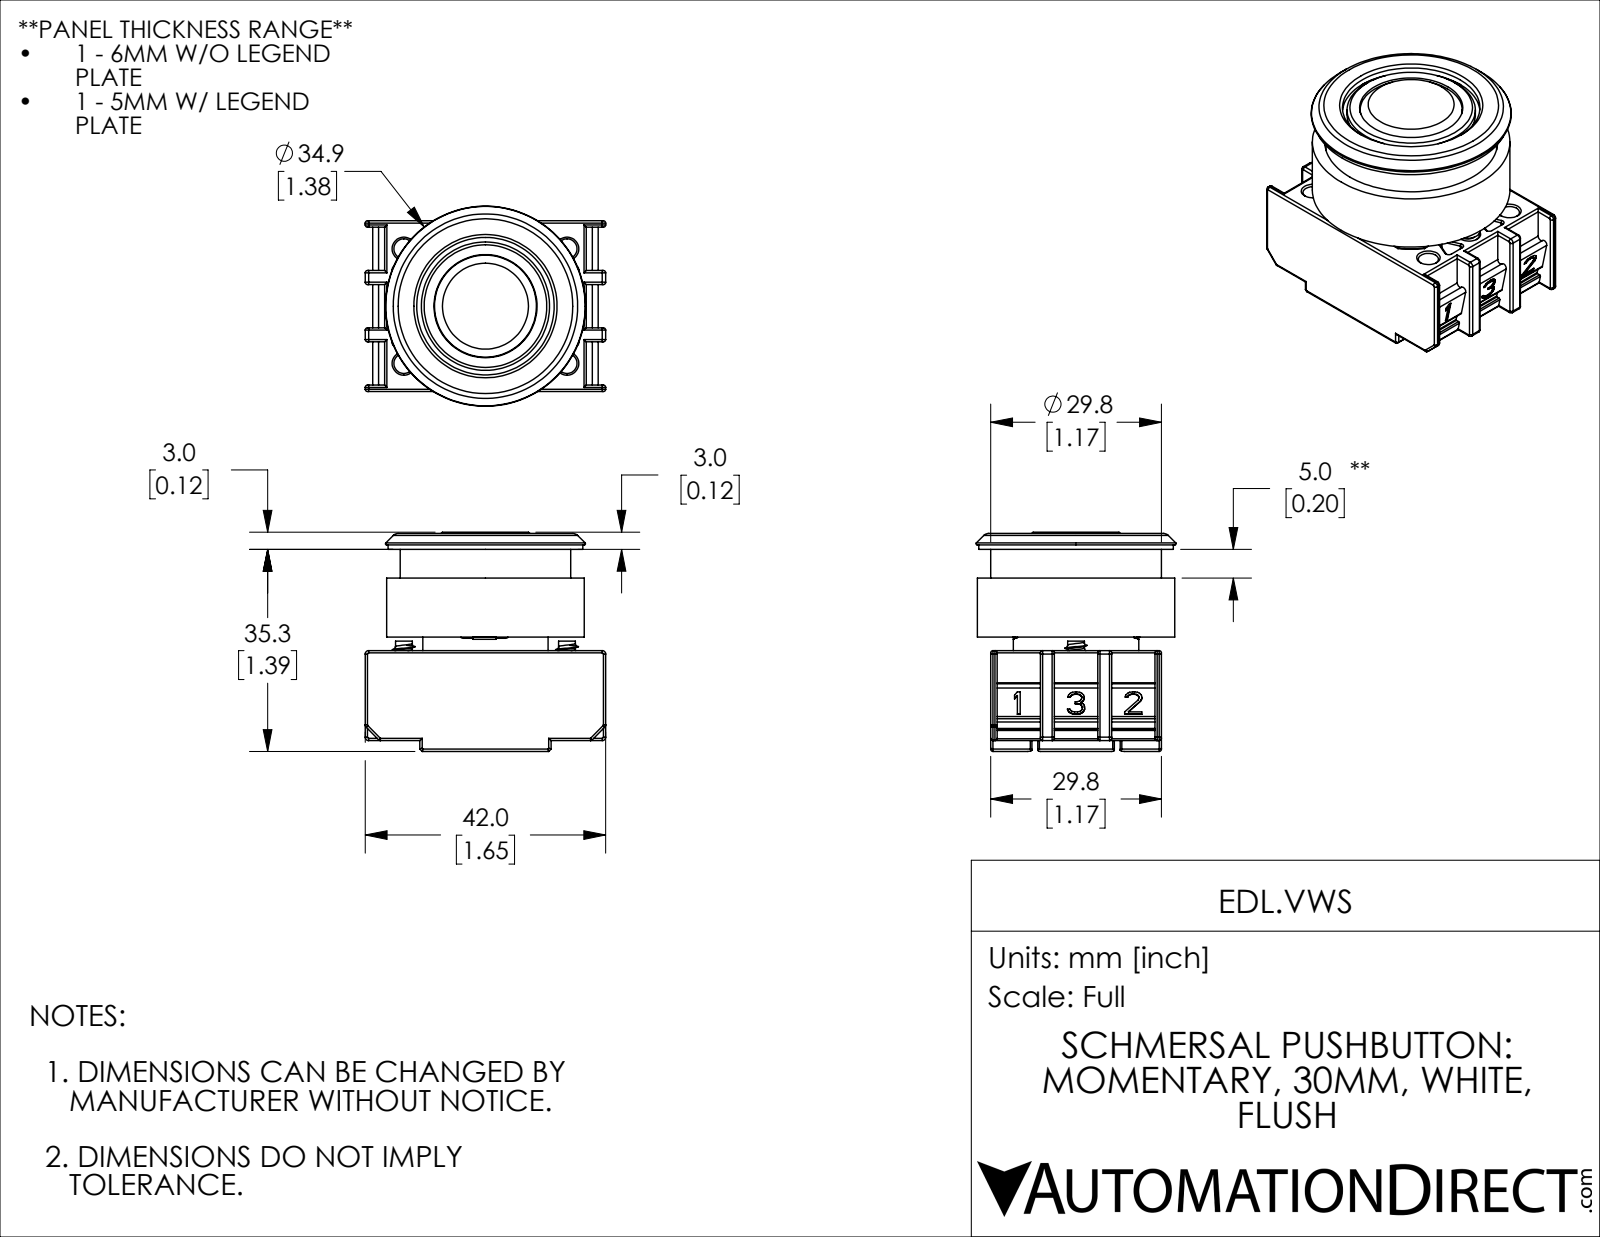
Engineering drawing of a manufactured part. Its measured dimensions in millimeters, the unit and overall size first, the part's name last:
Units: millimetres
Overall size (bounding box): 42 × 38.25 × 34.93
Round holes (diameter × count): ⌀3.5 ×6, ⌀5.15 ×6, ⌀10.4 ×1, ⌀13.1 ×1, ⌀18 ×1, ⌀24 ×1, ⌀24.2 ×1, ⌀27 ×1, ⌀30.2 ×1
Round bosses / shafts (diameter × count): ⌀4.8 ×2, ⌀2.93 ×2, ⌀34.5 ×1, ⌀34 ×1, ⌀29.8 ×1, ⌀22.4 ×1, ⌀21.9 ×1, ⌀17.8 ×1
Partial cylindrical surfaces — rounded edges, fillets, slot ends (radius × count): R0.4 ×112, R0.3 ×48, R0.2 ×32, R0.6 ×8, R0.5 ×6, R0.1 ×2, R0.6 ×2, R0.8 ×2
Main face-to-face distances: 29.8, 16.1, 19.95, 2.35, 10, 5, 1.9, 18.45, 10.3, 15.7
Hole centre spacings: 10, 17.41, 30.2, 28.5, 14.25, 20, 34.82
Volume: 25 195 mm³ · Surface area: 19 662 mm²
Bodies: 5 solids, 1372 faces (506 planar, 465 cylindrical, 401 other)
Part name (STEP PRODUCT): EDL.VWS
STEP written by: SolidWorks 2019 (CONFIG_CONTROL_DESIGN)
